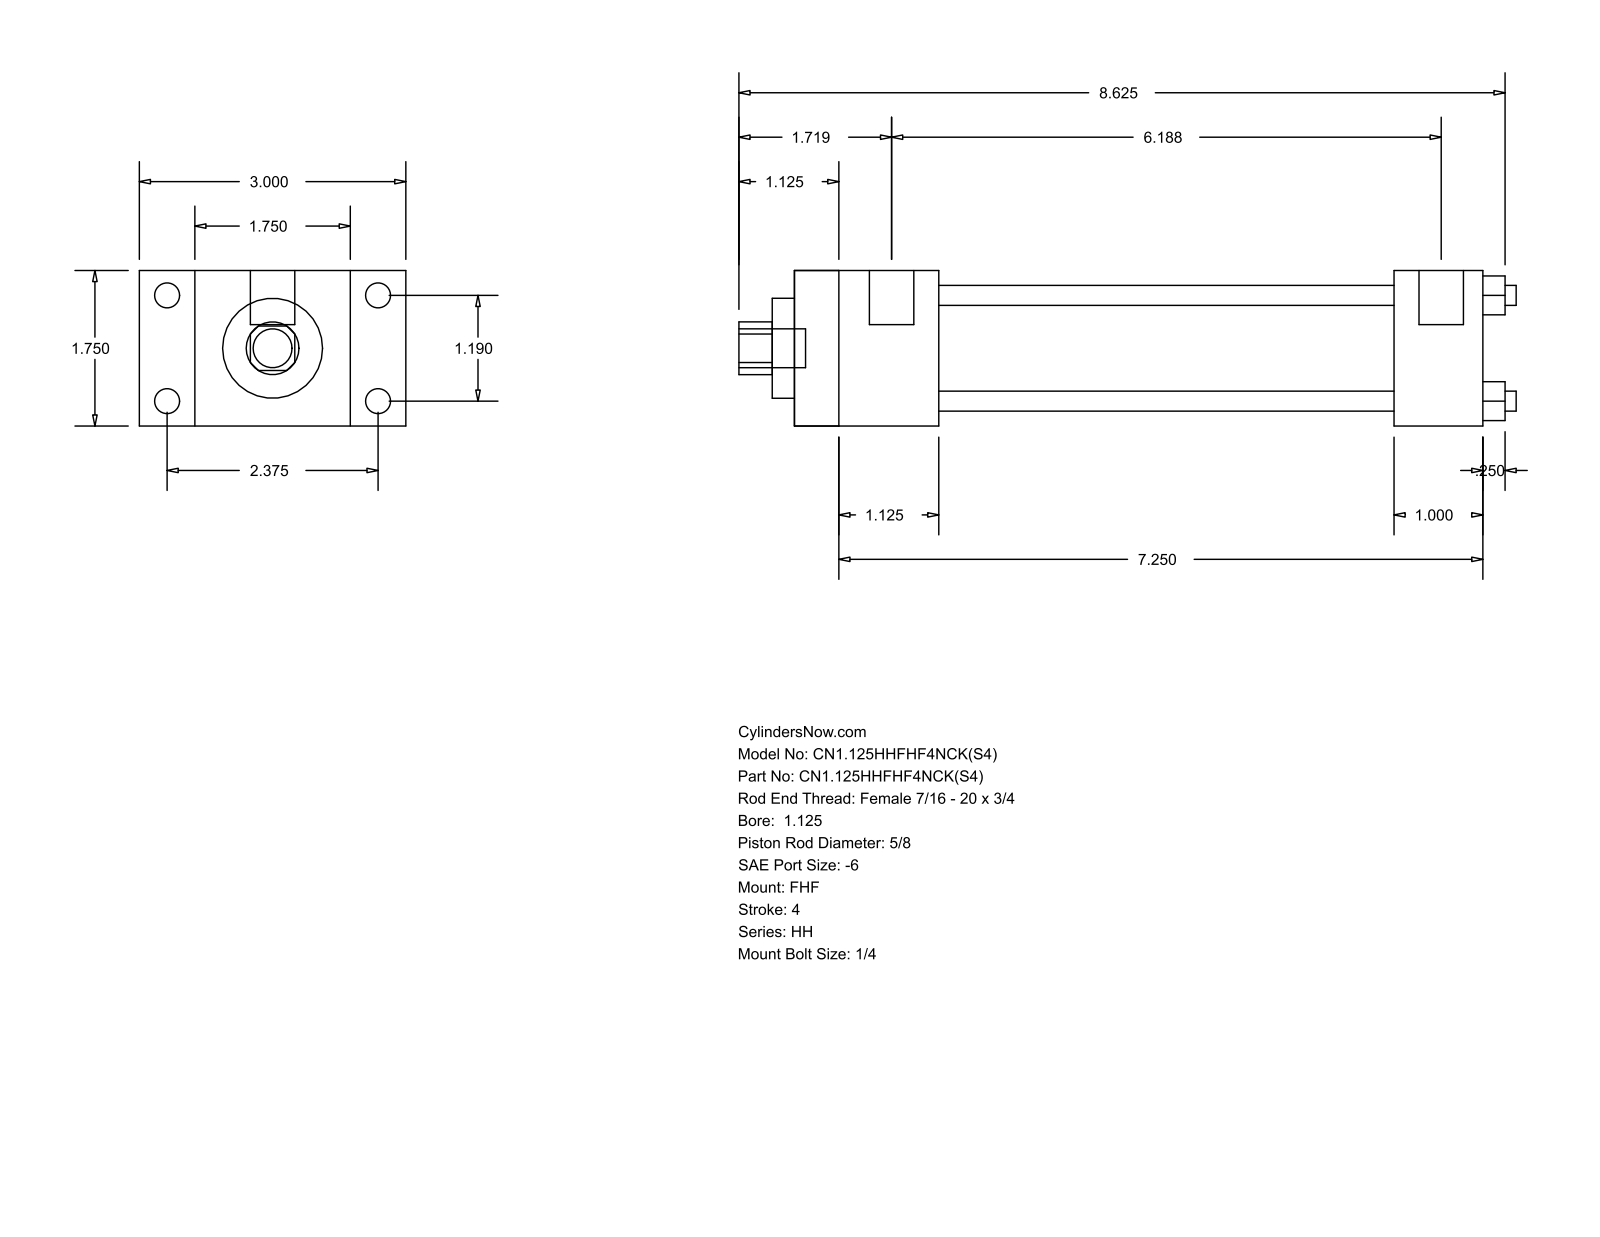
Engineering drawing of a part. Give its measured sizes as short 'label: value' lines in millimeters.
name: HH_FHF__0112_0.625
written by: GSSL Pune (CONFIG_CONTROL_DESIGN)
unit: mm
bodies: 0 solids, 88 faces (60 planar, 28 cylindrical, 0 other)
size: 222.25 × 76.2 × 44.45
holes: 4× ⌀5.71, 1× ⌀15.88, 1× ⌀28.57, 1× ⌀34.92
bosses: 4× ⌀7.14, 4× ⌀5.56, 2× ⌀12.7, 1× ⌀11.11
rounds: 1× R7.54
face distances: 44.46, 15.87, 60.33, 41.27, 76.2, 196.84, 155.57, 171.44, 130.17, 25.4
hole spacings: 21.37, 30.22, 42.74
